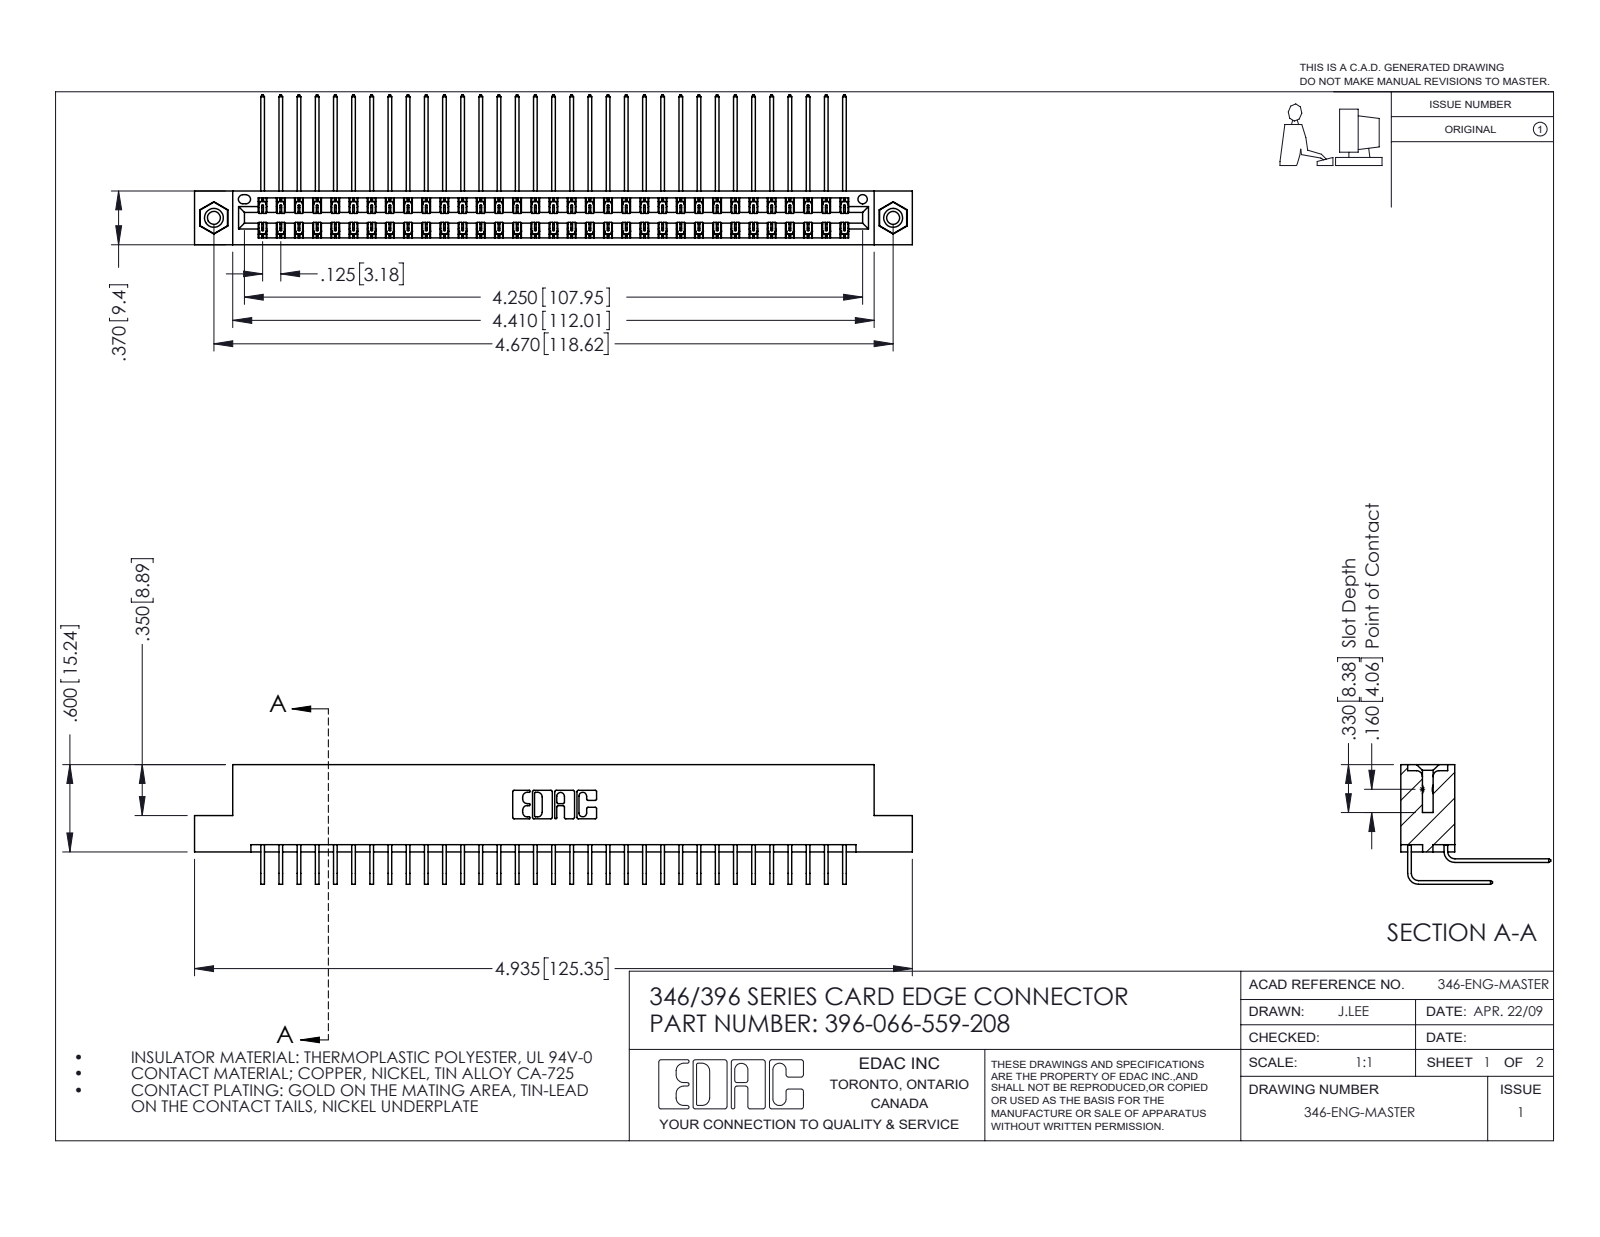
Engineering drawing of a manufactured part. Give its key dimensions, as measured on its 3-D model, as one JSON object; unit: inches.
{"part_name": "345-292-001_559 Tail - 2; 396-066-559-208; 345-292-001_558 559 Tail - 1; 346 Part_Flush Mounting Lugs - 0.156 Dia-TI (+1 more)", "step_written_by": "SolidWorks 2016 (CONFIG_CONTROL_DESIGN)", "units": "inches", "bodies": {"solids": 69, "faces": 3746, "planar": 2550, "cylindrical": 1180, "other": 16}, "overall_size": [4.935, 1.03, 0.823], "volume_in3": 0.764, "surface_area_in2": 29.33, "round_holes": [[0.089, 2], [0.125, 2], [0.156, 2], [0.064, 1]], "round_bosses_or_shafts": [[0.155, 2]], "partial_cylinders_radius": [[0.006, 99], [0.01, 22], [0.007, 6], [0.031, 6], [0.026, 3], [0.014, 2], [0.022, 2], [0.024, 2]], "face_to_face_distances": [0.048, 0.322, 0.025, 0.37, 0.25, 0.072, 0.298, 0.275, 0.148, 0.222], "hole_center_spacings": [0.246, 4.462, 4.67]}
